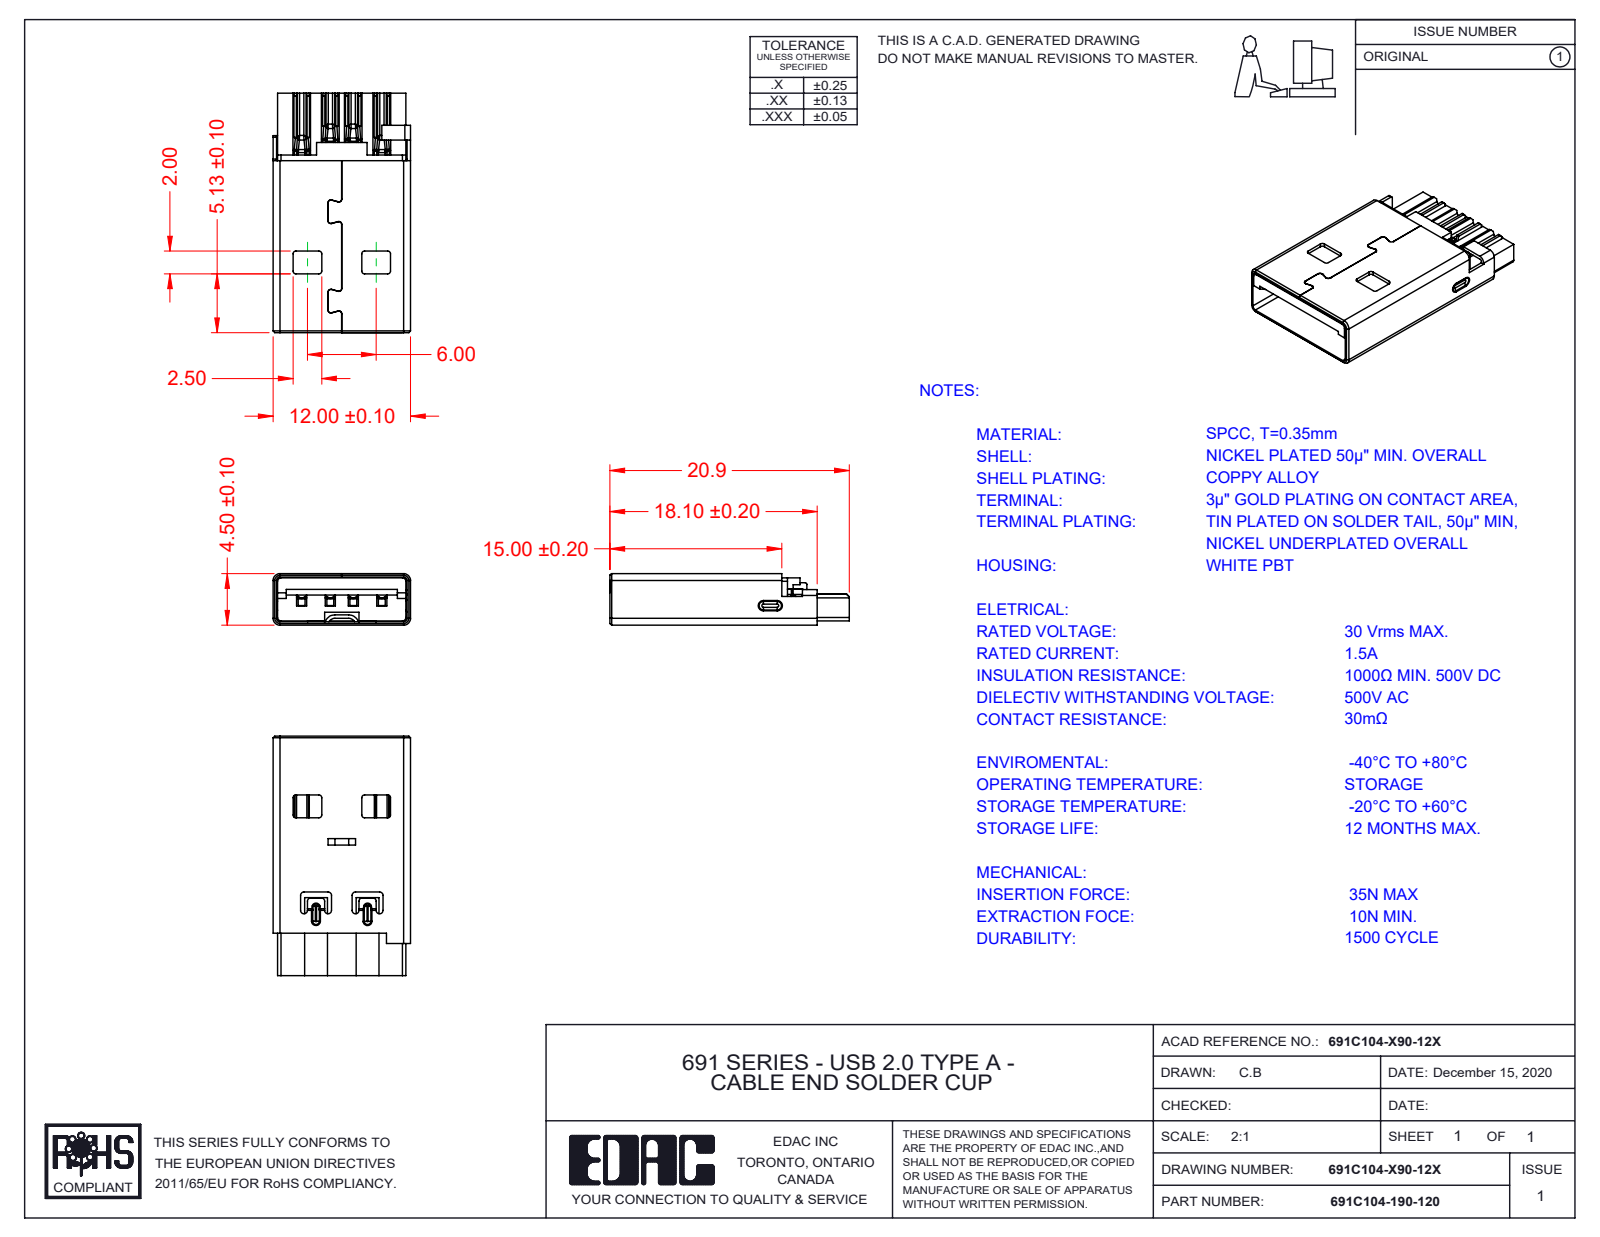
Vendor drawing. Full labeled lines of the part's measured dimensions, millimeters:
Part name (STEP PRODUCT): Contact 2 691C104-X90-12X; Insulator 691C104-X90-12X_White; Shell 691C104-X90-12X; Contact 1 691C104-X90-12X (+1 more)
STEP written by: SolidWorks 2020 (AUTOMOTIVE_DESIGN)
Units: millimetres
Bodies: 6 solids, 999 faces (476 planar, 202 cylindrical, 321 other)
Overall size (bounding box): 20.9 × 12 × 4.5
Volume: 630 mm³ · Surface area: 2 247 mm²
Partial cylindrical surfaces — rounded edges, fillets, slot ends (radius × count): R0.3 ×29, R0.25 ×24, R0.2 ×13, R0.15 ×11, R0.4 ×11, R0.1 ×10, R0.6 ×10, R0.35 ×8
Main face-to-face distances: 4.2, 3.83, 4.13, 0.37, 4.5, 3.9, 11.7, 3.76, 0.4, 11.6
